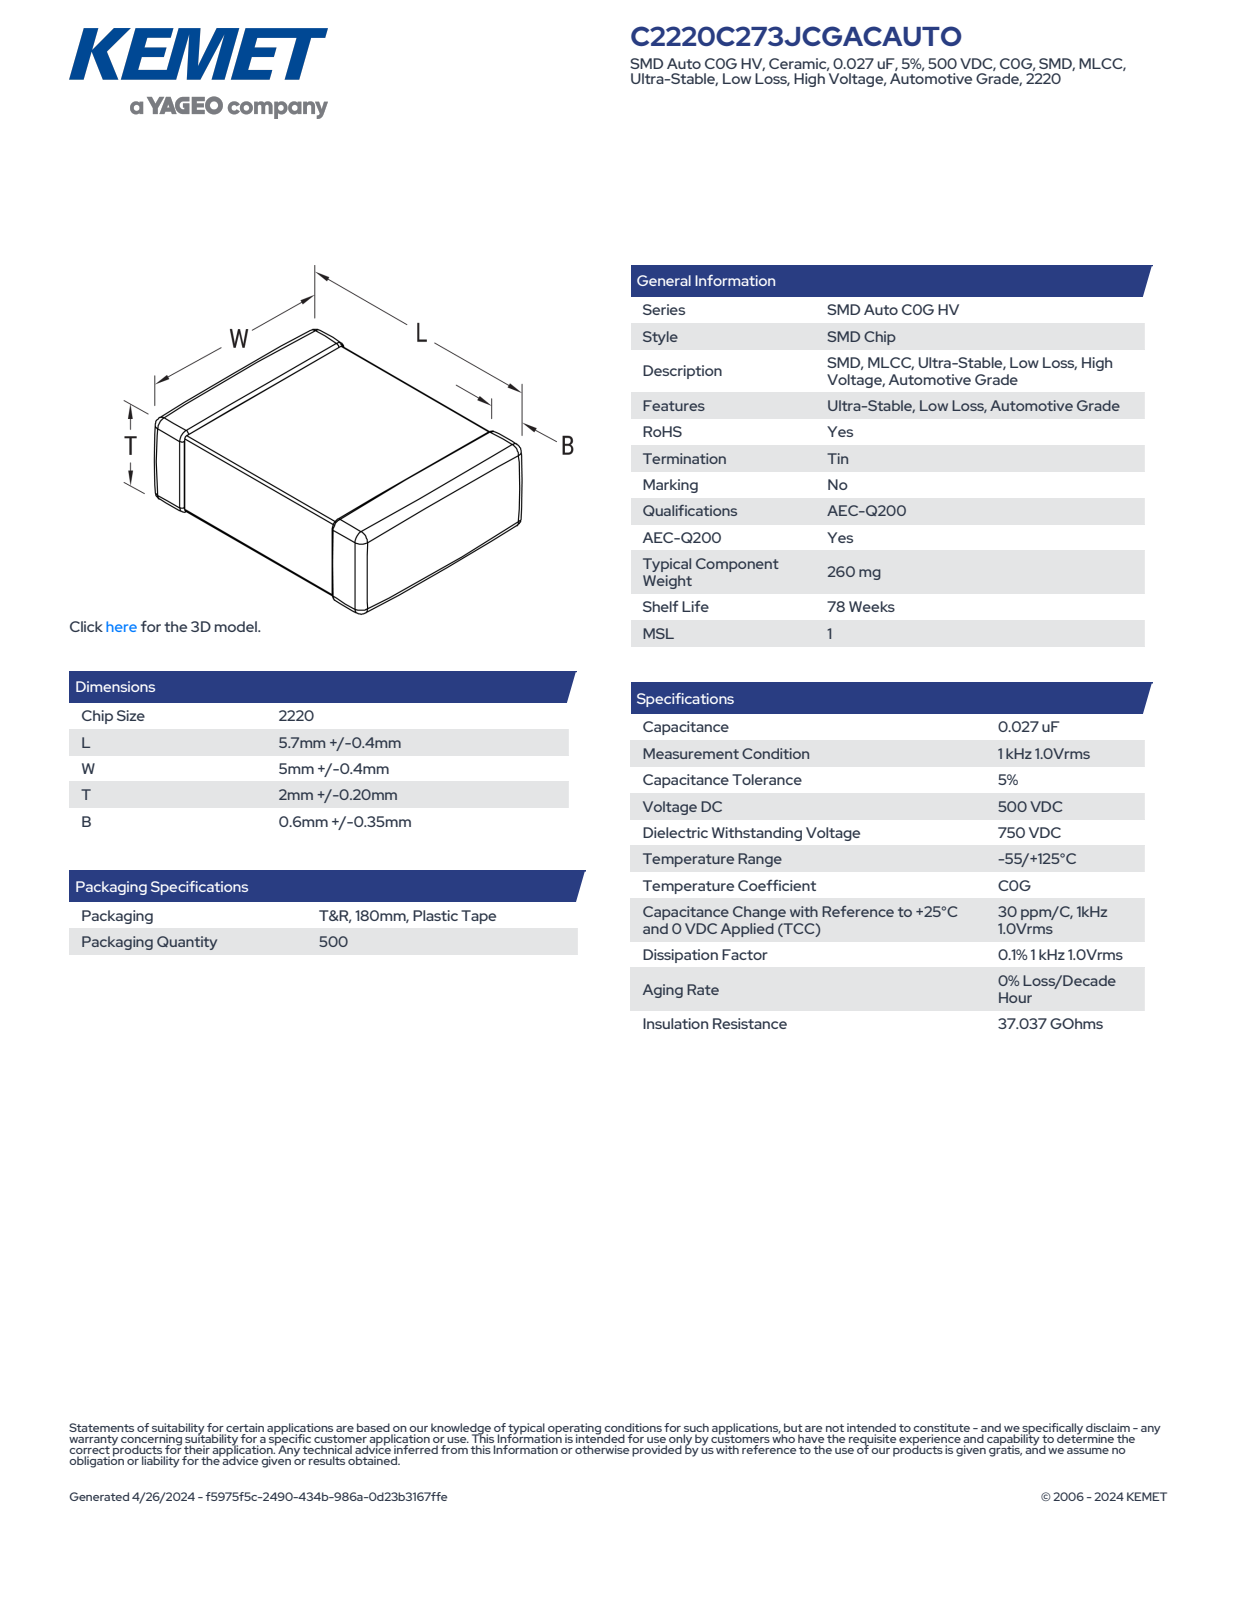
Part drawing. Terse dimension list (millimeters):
name: CCS_CCSTDNOS_2220_L6.1W5.4T2.2B0.95
written by: SolidWorks 2014 (AUTOMOTIVE_DESIGN)
unit: mm
bodies: 4 solids, 125 faces (71 planar, 38 cylindrical, 16 other)
size: 6.1 × 5.4 × 2.2
volume: 65 mm³; area: 113 mm²
rounds: 24× R0.11
face distances: 1.98, 2.09, 6.1, 2.2, 5.18, 5.29, 5.4, 2.66, 2.74, 2.55
